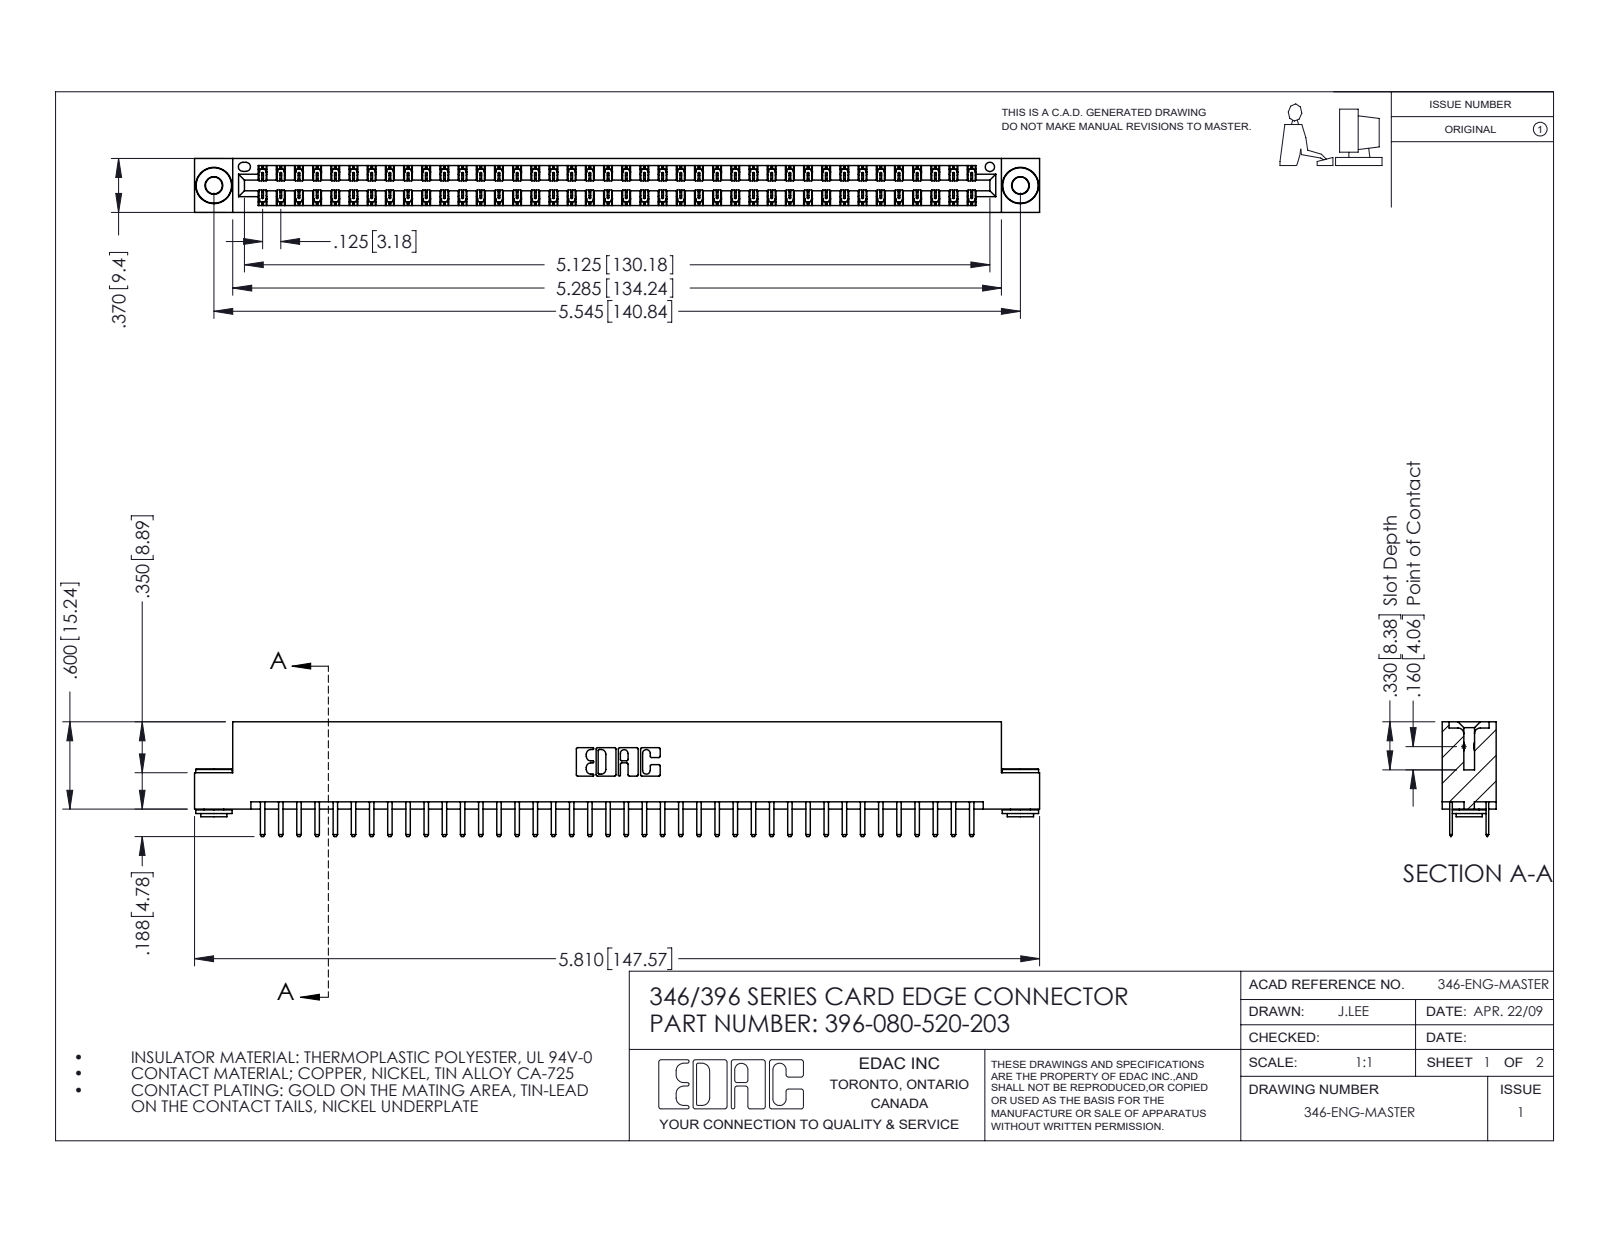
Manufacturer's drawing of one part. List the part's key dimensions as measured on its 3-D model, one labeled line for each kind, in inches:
Part name (STEP PRODUCT): 345-292-001_345-293-120; 346 Part_Flush Mounting Lugs - 0.156 Dia-TH; 345-250-002_345-250-002-102; 396-080-520-203
STEP written by: SolidWorks 2016 (CONFIG_CONTROL_DESIGN)
Units: inches
Bodies: 83 solids, 4640 faces (3046 planar, 1586 cylindrical, 8 other)
Overall size (bounding box): 5.81 × 0.788 × 0.37
Volume: 0.876 in³ · Surface area: 30.75 in²
Round holes (diameter × count): ⌀0.116 ×2, ⌀0.156 ×2, ⌀0.064 ×1
Round bosses / shafts (diameter × count): ⌀0.25 ×2, ⌀0.18 ×2, ⌀0.136 ×2
Partial cylindrical surfaces — rounded edges, fillets, slot ends (radius × count): R0.006 ×120, R0.01 ×84, R0.01 ×22, R0.007 ×6, R0.031 ×6, R0.026 ×3, R0.014 ×2, R0.022 ×2
Main face-to-face distances: 0.048, 0.322, 0.25, 0.37, 0.025, 0.275, 0.072, 0.298, 0.148, 0.222
Hole centre spacings: 0.246, 5.336, 5.545
